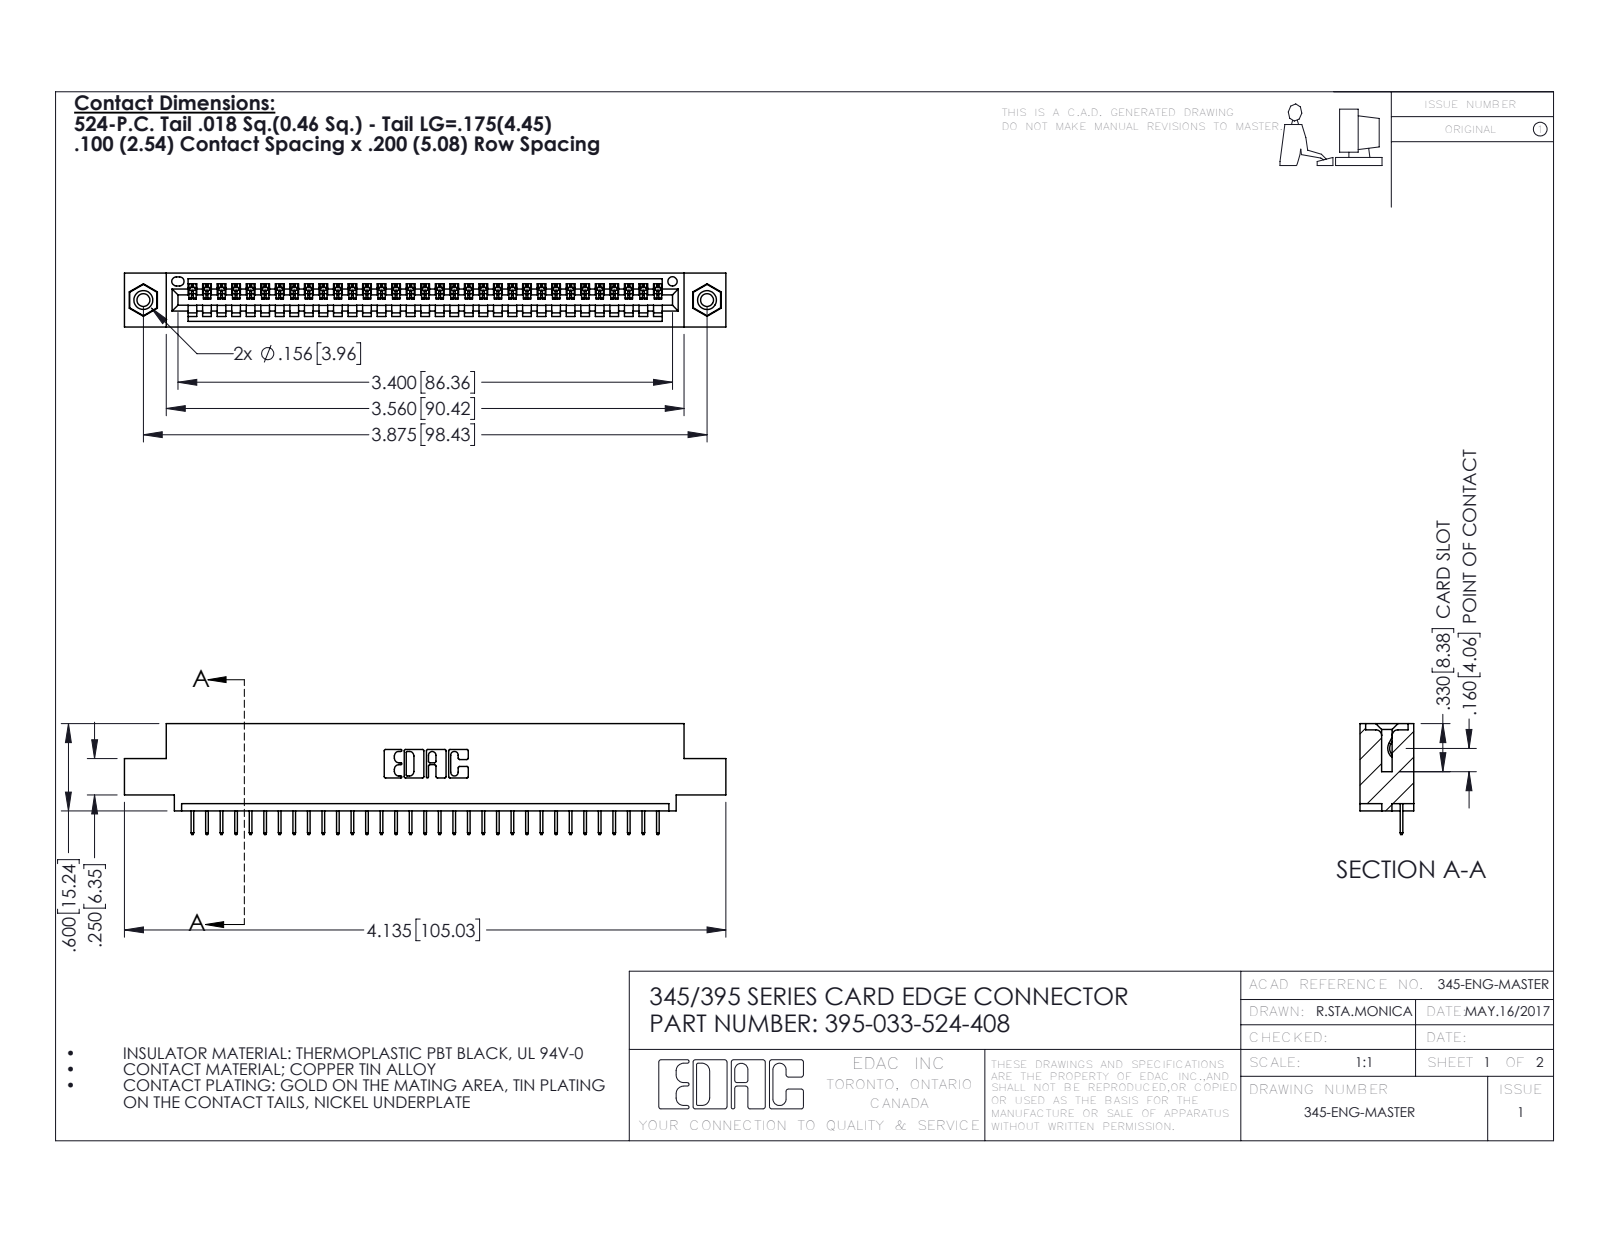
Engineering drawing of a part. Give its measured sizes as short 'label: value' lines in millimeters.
name: 395-033-524-408; 345-250-001_345-250-003-102; 345 Part_0.110 Offset - 0.156 Dia-TI; 345-292-001_345-293-124
written by: SolidWorks 2016 (CONFIG_CONTROL_DESIGN)
unit: mm
bodies: 36 solids, 2236 faces (1634 planar, 586 cylindrical, 16 other)
size: 105 × 19.4 × 9.4
volume: 9 680 mm³; area: 12 440 mm²
holes: 2× ⌀2.3, 2× ⌀3.2, 2× ⌀4, 1× ⌀1.6
bosses: 2× ⌀3.9
rounds: 66× R0.2, 22× R0.3, 6× R0.2, 6× R0.8, 3× R0.7, 2× R0.8, 2× R1, 1× R0.4
face distances: 1.8, 7.6, 9.4, 5.1, 2.5, 6.9, 0.6, 5.7, 1.8, 3.8
hole spacings: 6.9, 92.5, 98.4
